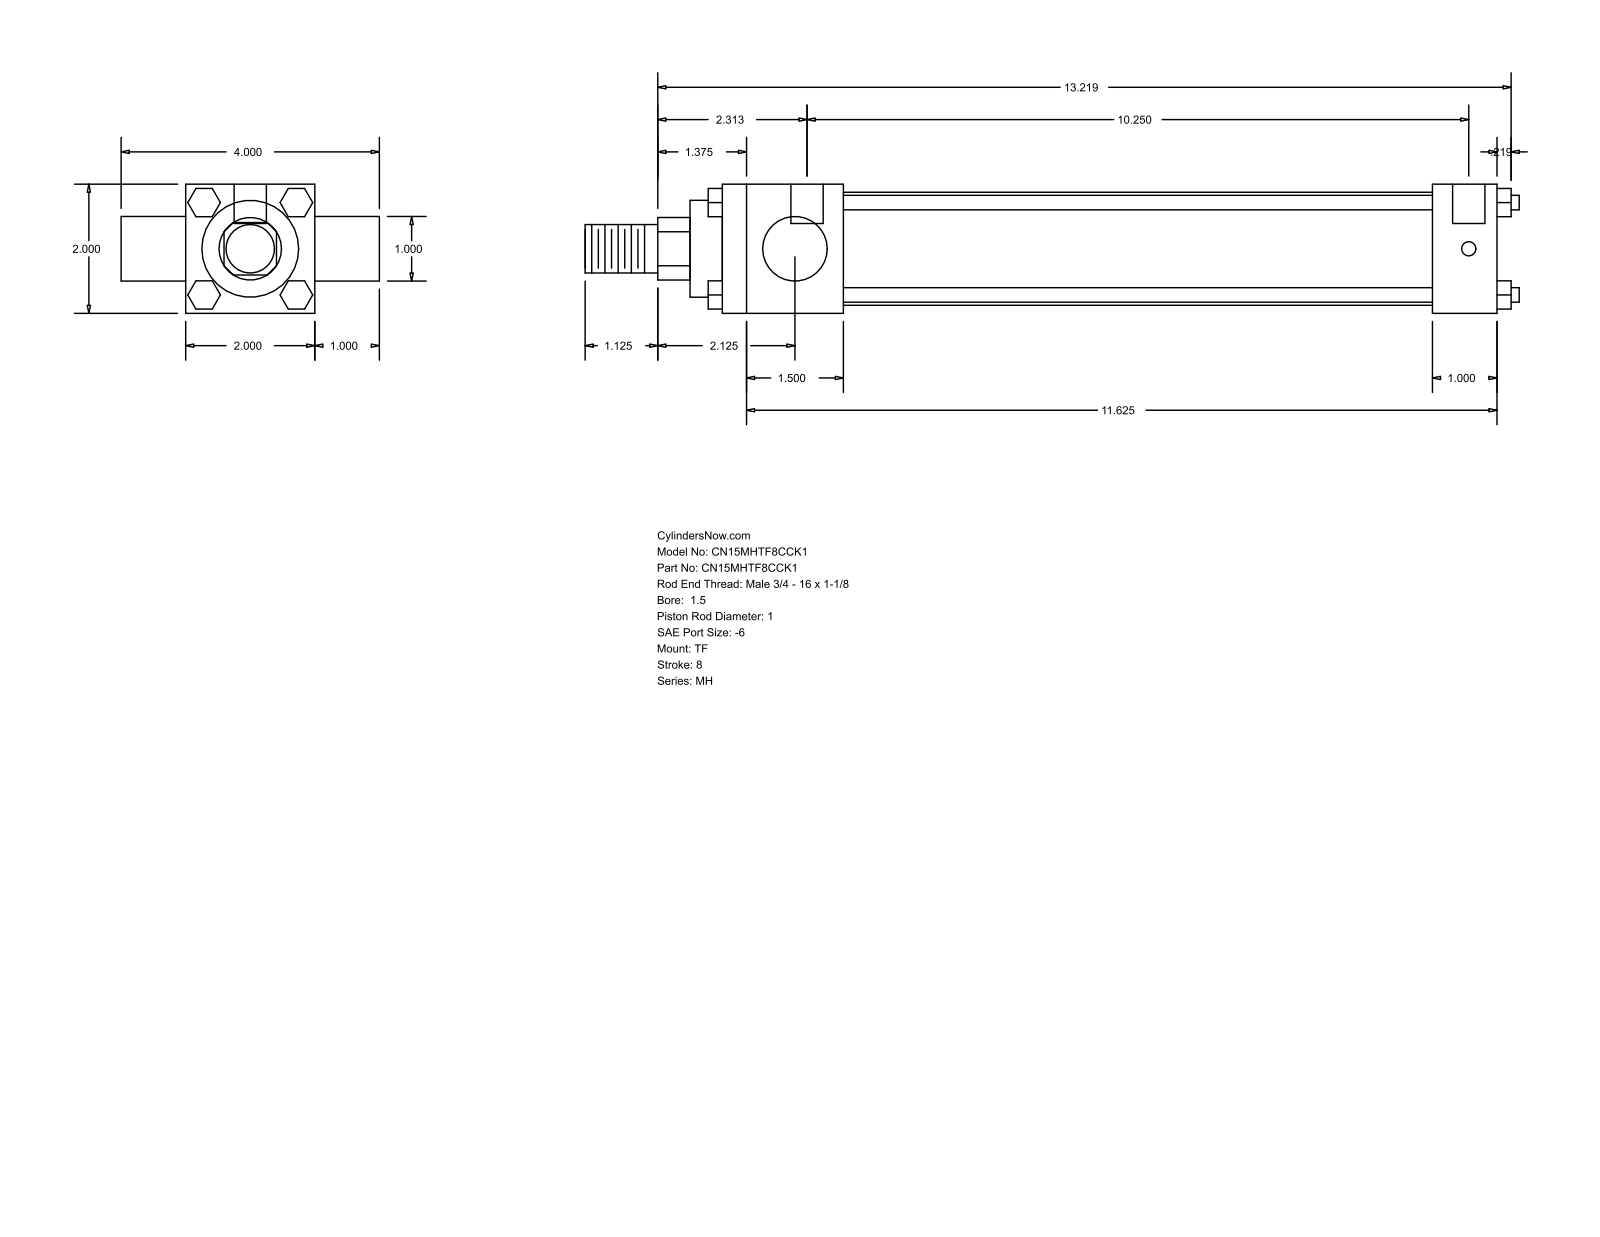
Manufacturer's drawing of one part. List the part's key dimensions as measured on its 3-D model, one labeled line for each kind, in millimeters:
Part name (STEP PRODUCT): MH_TF__0150_1
STEP written by: GSSL Pune (CONFIG_CONTROL_DESIGN)
Units: millimetres
Bodies: 0 solids, 120 faces (92 planar, 28 cylindrical, 0 other)
Overall size (bounding box): 367.51 × 101.6 × 50.8
Round holes (diameter × count): ⌀5.56 ×3, ⌀12.7 ×2
Round bosses / shafts (diameter × count): ⌀5.71 ×4, ⌀25.4 ×2, ⌀44.45 ×1, ⌀38.1 ×1, ⌀19.05 ×1
Partial cylindrical surfaces — rounded edges, fillets, slot ends (radius × count): R12.29 ×1
Main face-to-face distances: 50.8, 25.4, 304.8, 76.2, 47.63, 257.17, 279.4, 231.77, 101.6, 12.7
Hole centre spacings: 3.18, 260.35, 263.53
